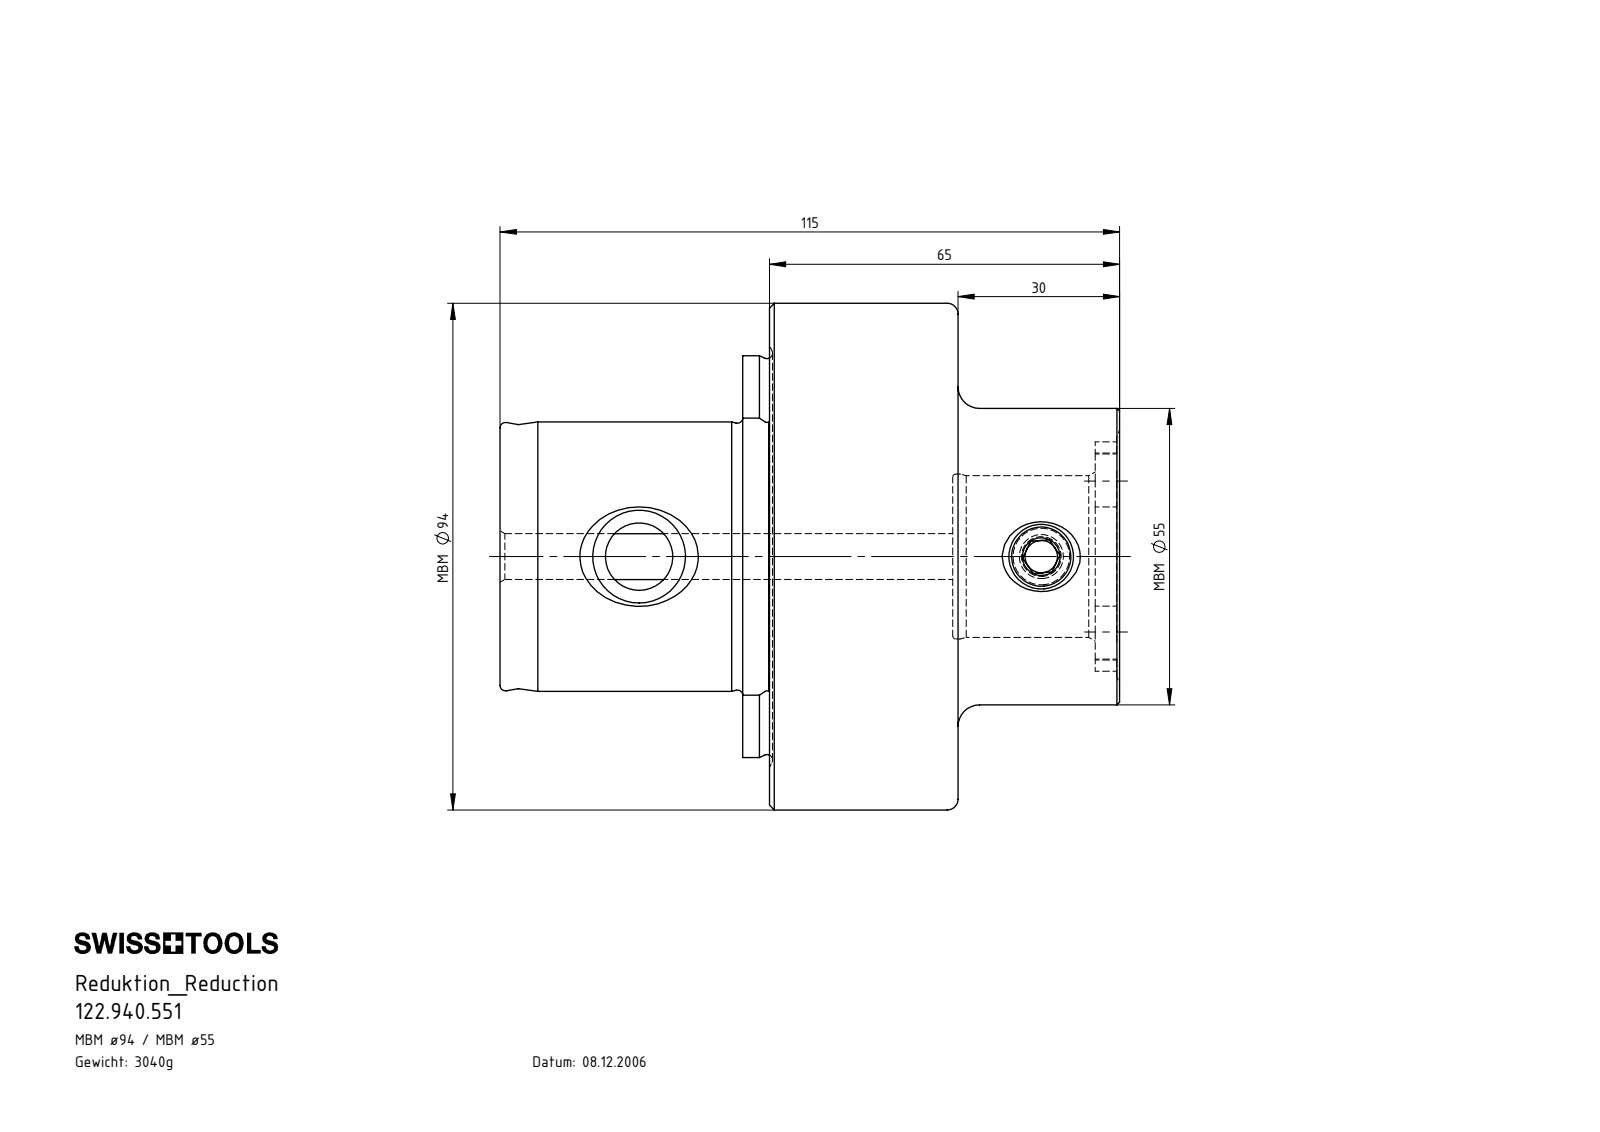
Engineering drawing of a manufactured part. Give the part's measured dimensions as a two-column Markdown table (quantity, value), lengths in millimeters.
| quantity | value |
| --- | --- |
| part name | MB9-MB5.K01.065_C; MB5-ER1.001.017_A; 122.940.551 |
| STEP written by | SolidWorks 2017 (CONFIG_CONTROL_DESIGN) |
| units | millimeters |
| bodies | 2 solids, 135 faces (35 planar, 35 cylindrical, 65 other) |
| overall size | 115 × 94 × 94 |
| volume | 387 218 mm³ |
| surface area | 43 729 mm² |
| round holes (diameter × count) | 6 × 1, 8.5 × 1, 11 × 1, 12.5 × 1, 30 × 1, 30.6 × 1 |
| round bosses / shafts (diameter × count) | 94 × 1, 55 × 1, 50 × 1, 12 × 1 |
| partial cylindrical surfaces (radius × count) | 5.2 × 4, 18.5 × 1, 21.27 × 1, 37.27 × 1 |
| main face-to-face distances | 35, 50, 85, 45.05, 4.95, 39.95, 49.85, 4.8, 35.15, 84 |
| hole center spacings | 74.65 |
